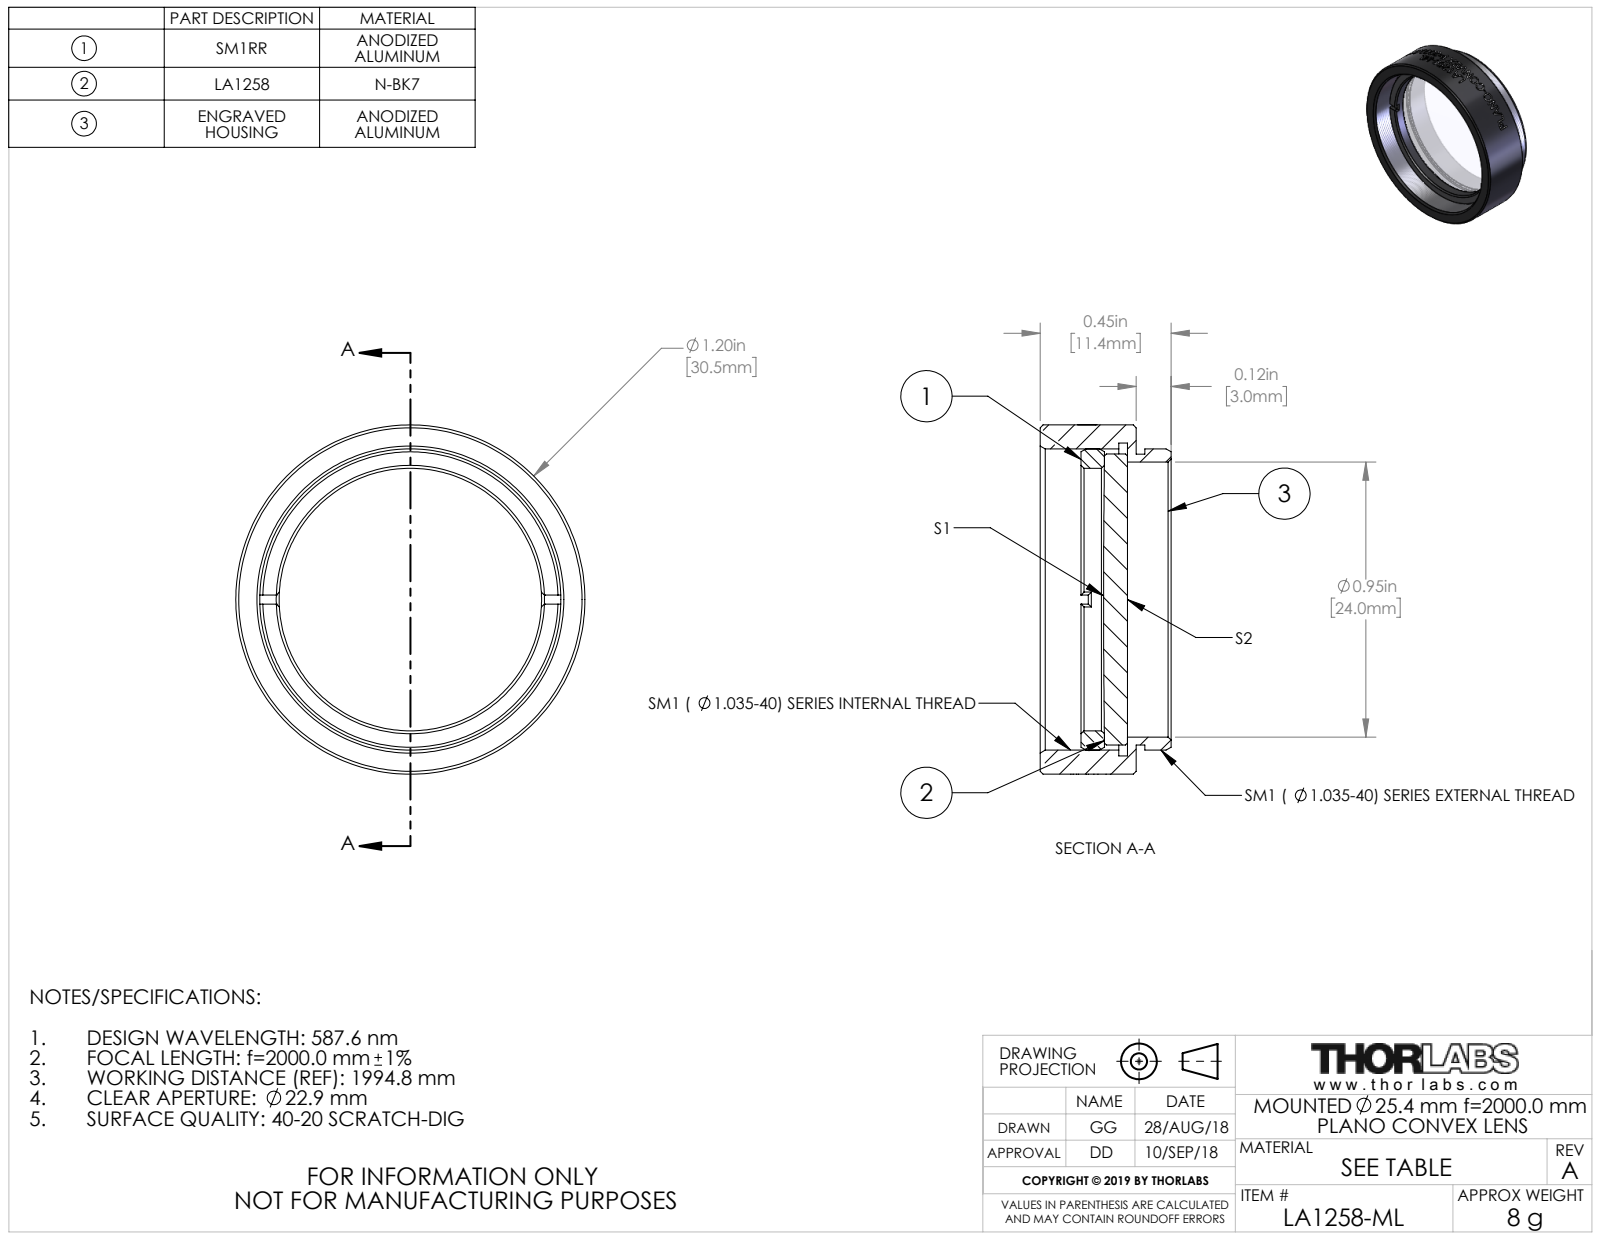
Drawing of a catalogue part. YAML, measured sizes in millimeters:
part_name: "TTN162139-E0W"
step_written_by: "SolidWorks 2018 (CONFIG_CONTROL_DESIGN)"
units: millimeters
bodies: {solids: 3, faces: 141, planar: 20, cylindrical: 93, other: 28}
overall_size: [30.48, 30.48, 11.43]
volume: 3113
surface_area: 4296
round_holes:
  - {diameter: 22.91, count: 1}
  - {diameter: 24, count: 1}
  - {diameter: 26.29, count: 1}
  - {diameter: 27.3, count: 1}
round_bosses_or_shafts:
  - {diameter: 30.48, count: 1}
  - {diameter: 26.29, count: 1}
  - {diameter: 25.4, count: 1}
  - {diameter: 25.37, count: 1}
face_to_face_distances: [0.77, 8.39, 7.62, 2.78, 2.01, 5.61, 4.81, 4.04, 2.03, 3.58]
